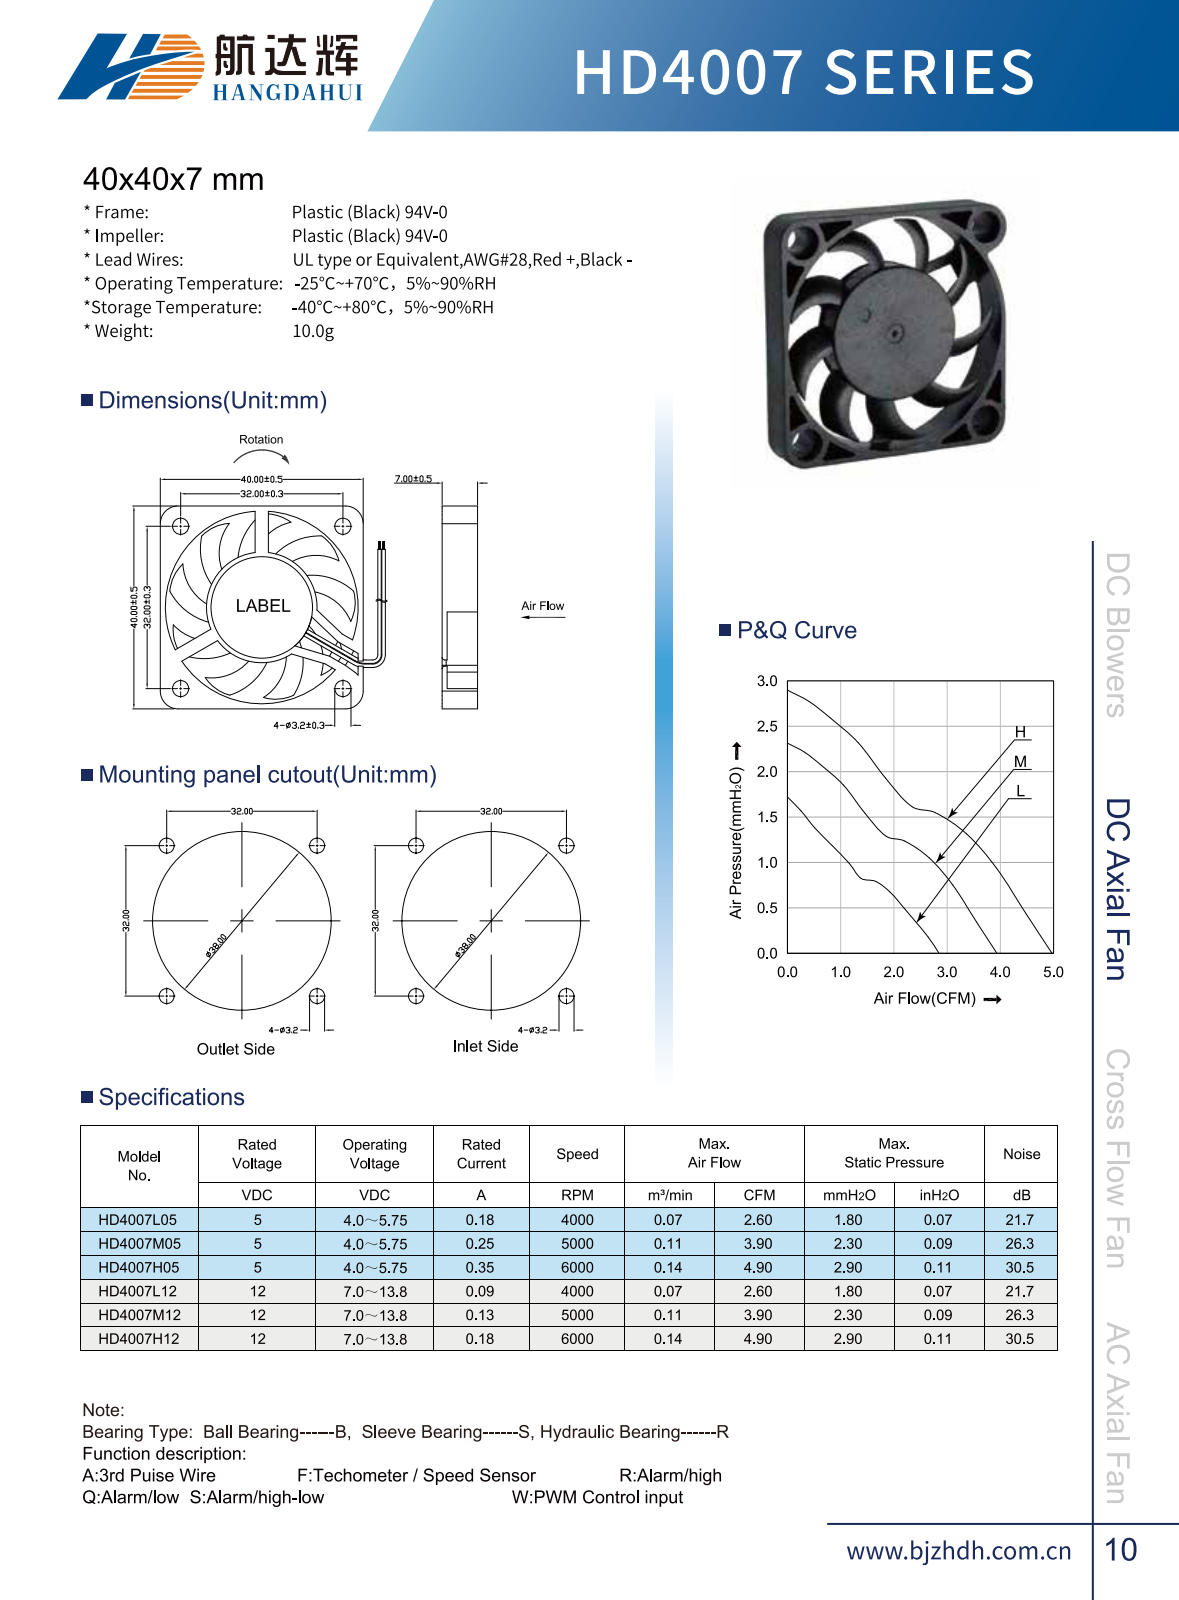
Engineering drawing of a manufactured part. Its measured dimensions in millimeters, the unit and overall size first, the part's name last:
Units: millimetres
Overall size (bounding box): 40 × 40 × 7.2
Round holes (diameter × count): ⌀3.2 ×4, ⌀5.2 ×4, ⌀38 ×1
Round bosses / shafts (diameter × count): ⌀22 ×1
Partial cylindrical surfaces — rounded edges, fillets, slot ends (radius × count): R0.2 ×21, R1.5 ×12, R3.6 ×4, R4 ×4, R0.5 ×2, R18.25 ×1, R20 ×1
Main face-to-face distances: 40, 6.3, 0.8, 39.2, 0.9, 7.2, 1.2, 5.1, 6, 38.4
Hole centre spacings: 22.63, 32, 45.25
Volume: 4 937 mm³ · Surface area: 6 191 mm²
Bodies: 1 solid, 207 faces (56 planar, 91 cylindrical, 60 other)
Part name (STEP PRODUCT): 53033118ybng
STEP written by: UGS - NX 4.0 (CONFIG_CONTROL_DESIGN)
